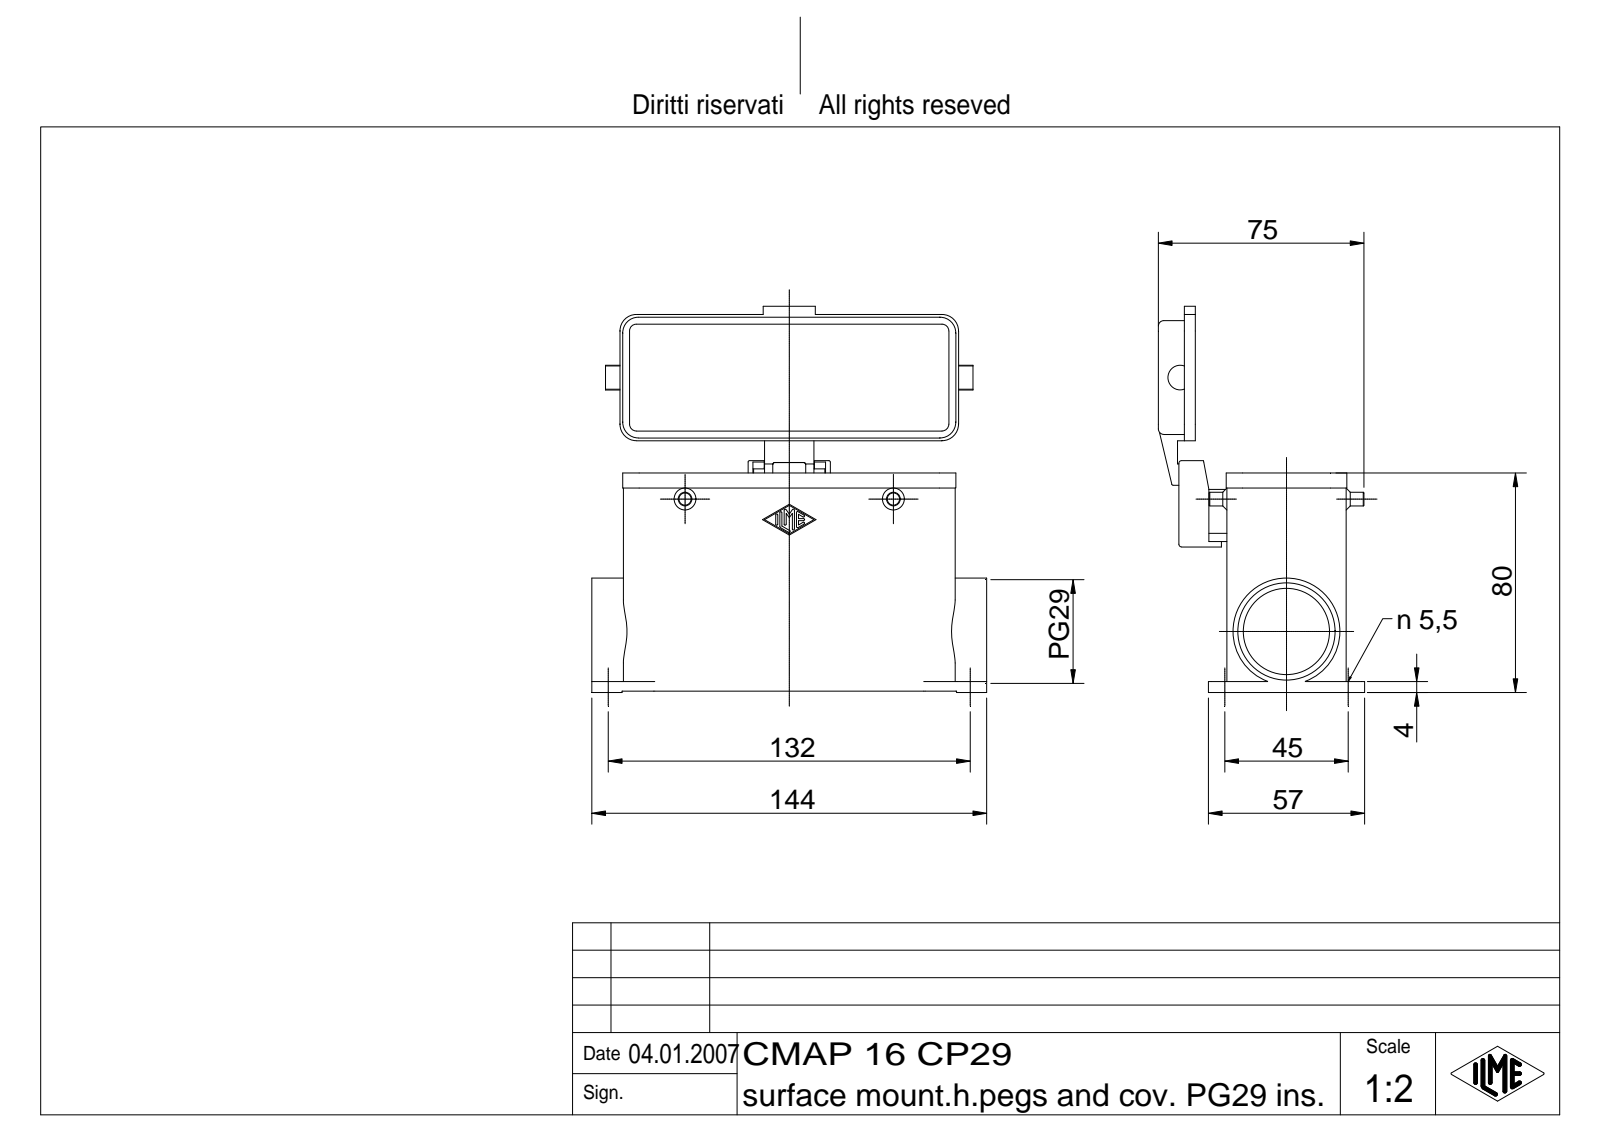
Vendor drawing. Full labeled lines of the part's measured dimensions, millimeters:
Part name (STEP PRODUCT): CMAP 16 CP29
STEP written by: Autodesk Inventor 7 (AUTOMOTIVE_DESIGN)
Units: millimetres
Bodies: 1 solid, 474 faces (197 planar, 166 cylindrical, 111 other)
Overall size (bounding box): 144 × 140.75 × 75.25
Volume: 146 803 mm³ · Surface area: 92 242 mm²
Round holes (diameter × count): ⌀5.5 ×4, ⌀4 ×1, ⌀5 ×1, ⌀31.48 ×1, ⌀35.48 ×1
Round bosses / shafts (diameter × count): ⌀5 ×2, ⌀3 ×2, ⌀38.98 ×1, ⌀7 ×1, ⌀4 ×1
Partial cylindrical surfaces — rounded edges, fillets, slot ends (radius × count): R0.38 ×14, R1 ×14, R6 ×12, R0.5 ×10, R0.7 ×8, R2 ×8, R2.5 ×4, R3 ×4
Main face-to-face distances: 3, 40.5, 43.5, 37.5, 2.5, 3.5, 22.5, 63, 66, 25.5
Hole centre spacings: 45, 132, 139.46
